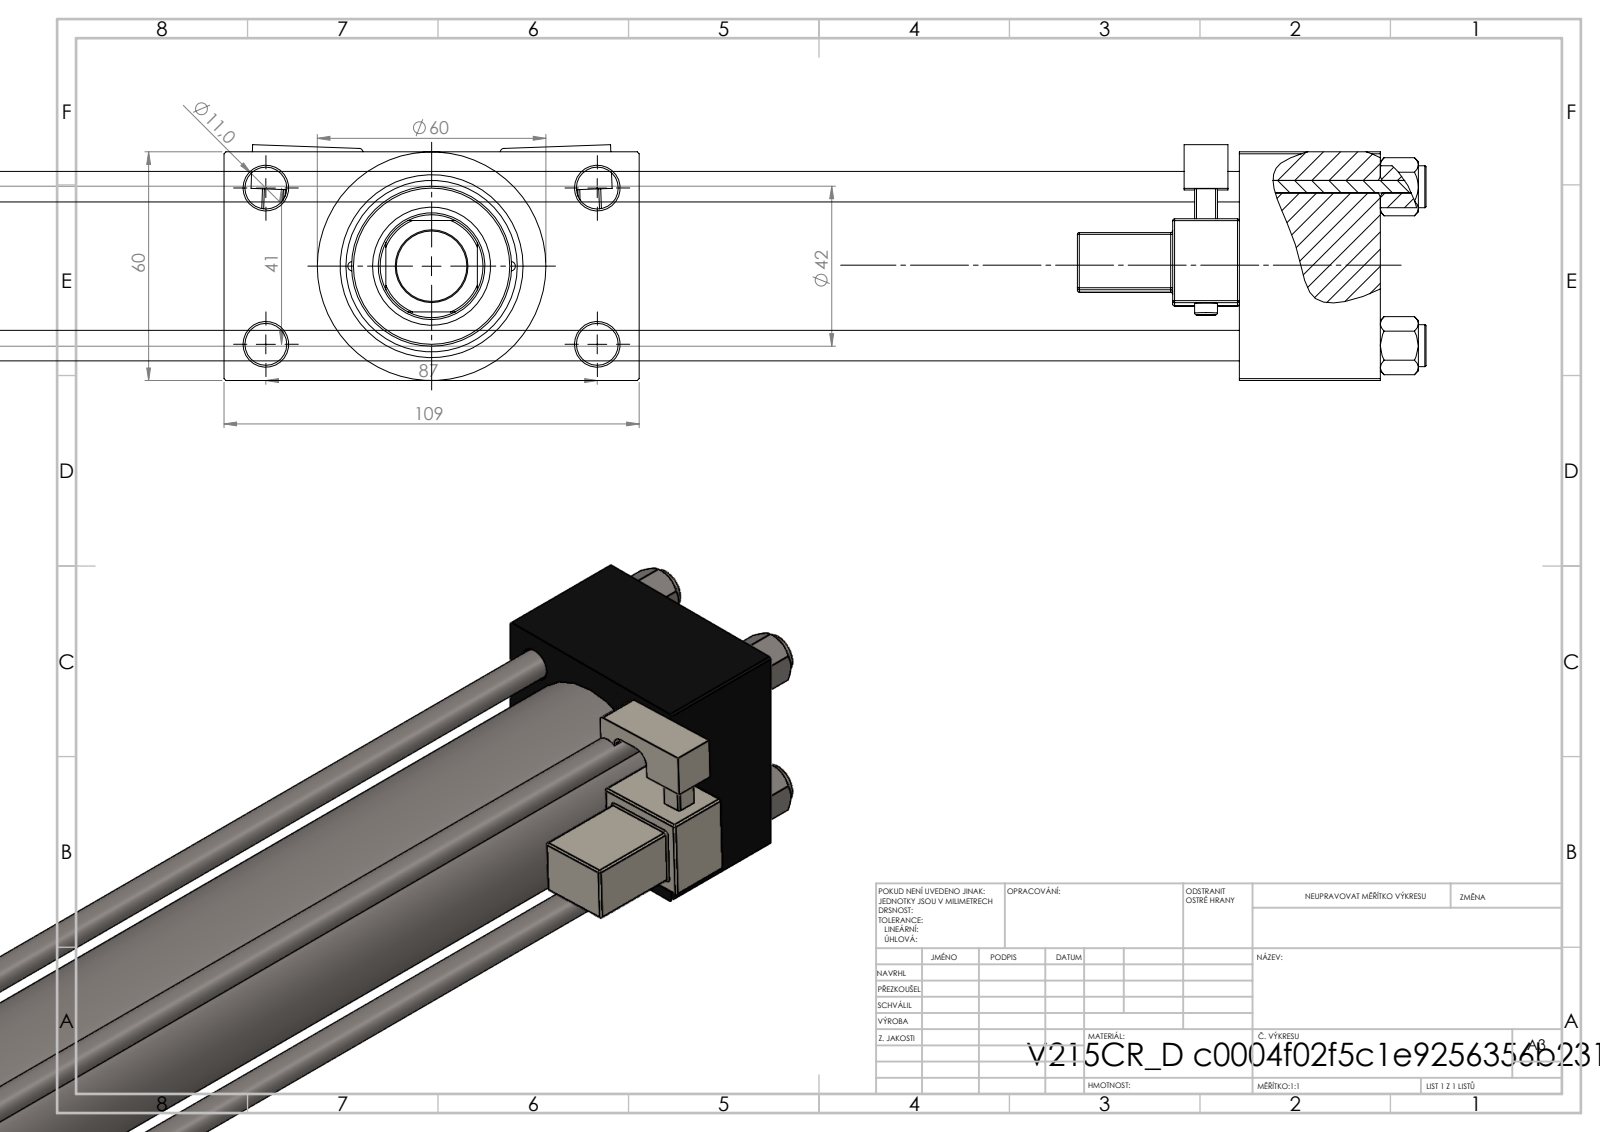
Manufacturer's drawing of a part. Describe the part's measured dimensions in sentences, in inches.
The part is named "V215CR_VCP_D; V215CR_D_Body; V215_VC_A; NUT_M5_D (+2 more)". Its 3-D file was written by "SolidWorks 2019 (CONFIG_CONTROL_DESIGN)". It is 13 solids with 1268 faces: 560 planar, 152 cylindrical and 556 other. Overall it measures 20.276 by 4.291 by 2.437 inches. Its volume is 59.36 cubic inches and its surface area 453.4 square inches. Round holes: 4 of diameter 0.315, 4 of diameter 0.433, 2 of diameter 0.098, 2 of diameter 0.276, 2 of diameter 0.656, 2 of diameter 0.945, 1 of diameter 0.728, 1 of diameter 1.102, 1 of diameter 1.22, 1 of diameter 1.575, 1 of diameter 1.772. Round bosses or shafts: 4 of diameter 0.433, 2 of diameter 0.236, 1 of diameter 2.362, 1 of diameter 1.811, 1 of diameter 1.654. Partial cylindrical surfaces (rounded edges, fillets, slot ends): 48 of radius 0.02, 2 of radius 0.039, 2 of radius 0.098, 2 of radius 0.157, 1 of radius 0.531. The main face-to-face distances are 2.362, 15.276, 0.965, 3.327, 1.457, 16.732, 18.425, 16.969, 1.693, 4.291. The hole center spacings are 0.821, 0.892, 1.161, 1.206, 1.642, 1.832, 1.856, 1.893.
